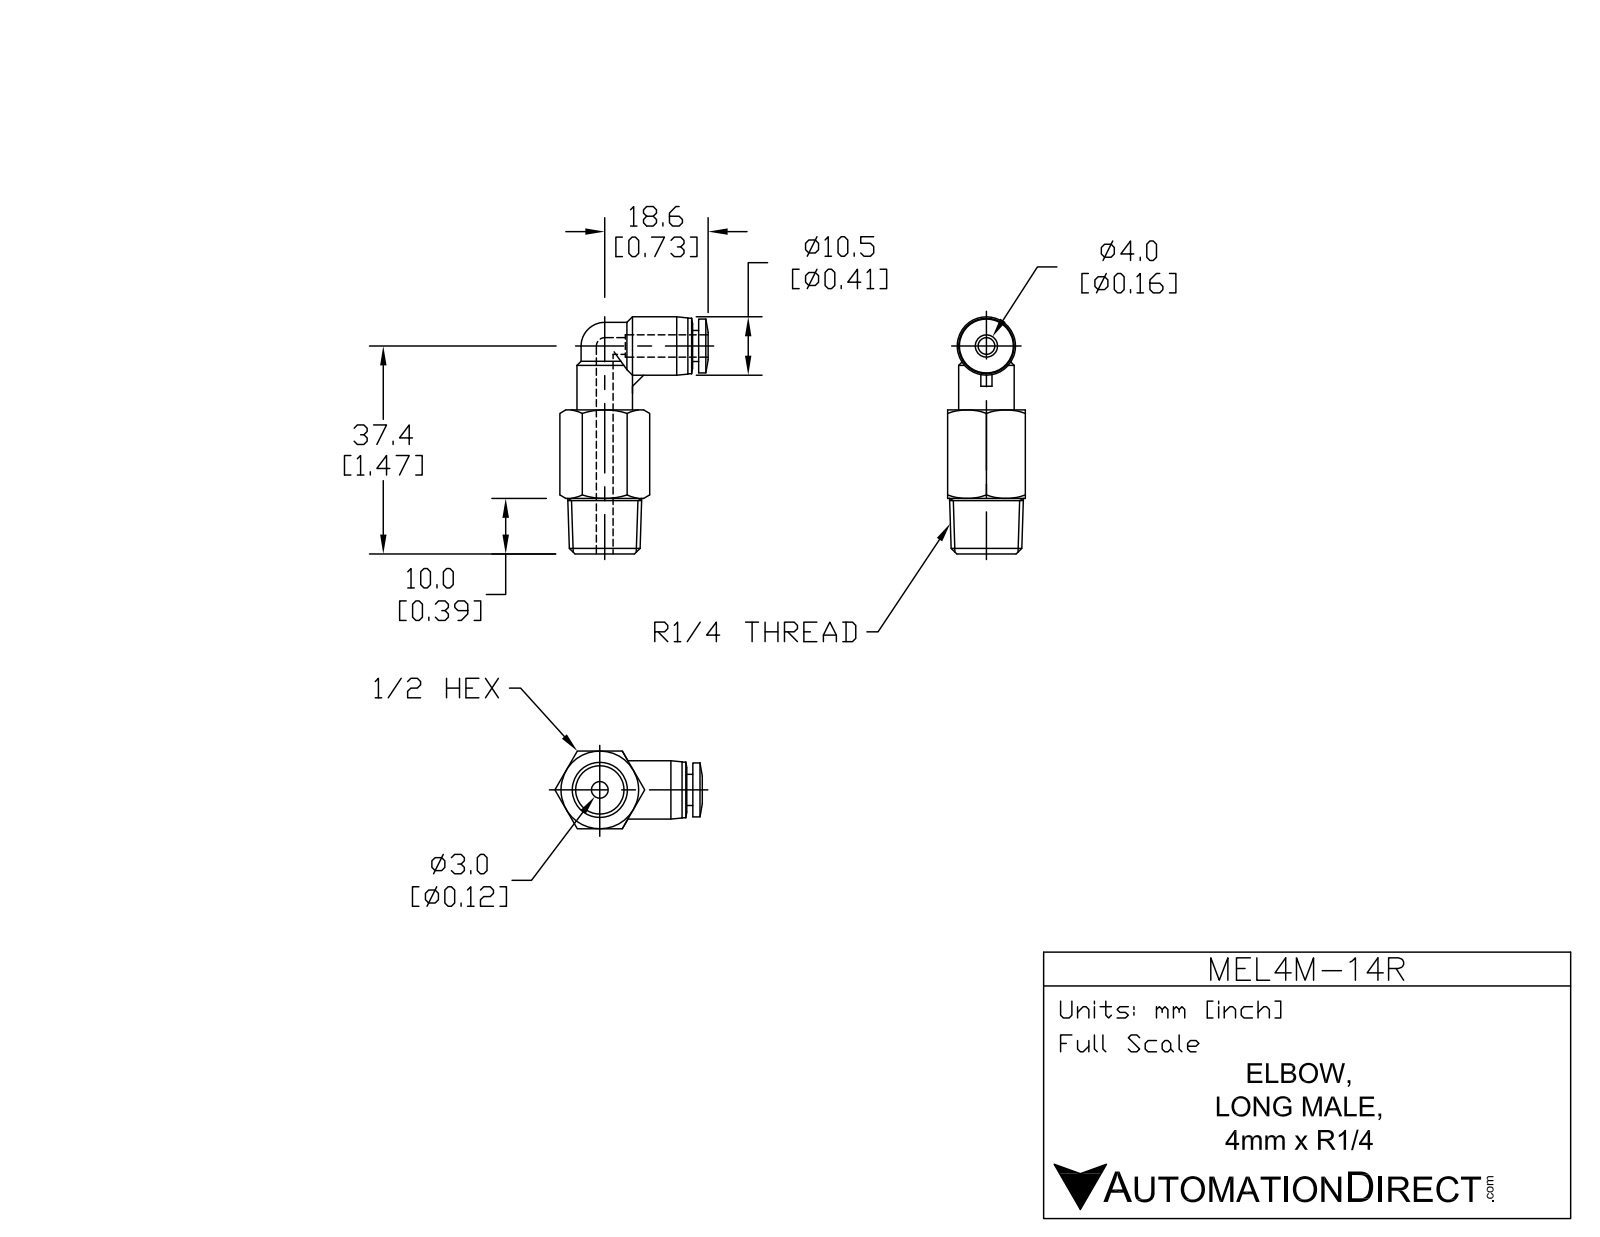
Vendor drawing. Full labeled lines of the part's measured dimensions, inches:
Part name (STEP PRODUCT): MEL4M-14R
STEP written by: SolidWorks 2015 (AUTOMOTIVE_DESIGN)
Units: inches
Bodies: 1 solid, 69 faces (17 planar, 19 cylindrical, 33 other)
Overall size (bounding box): 1.683 × 1.045 × 0.551
Volume: 0.346 in³ · Surface area: 4.686 in²
Round holes (diameter × count): ⌀0.118 ×2, ⌀0.169 ×1
Round bosses / shafts (diameter × count): ⌀0.394 ×2, ⌀0.413 ×1, ⌀0.382 ×1, ⌀0.22 ×1
Partial cylindrical surfaces — rounded edges, fillets, slot ends (radius × count): R0.167 ×2
Main face-to-face distances: 0.551, 1.024, 0.043, 0.394, 0.63, 0.472, 0.516, 0.236, 0.315, 0.079
